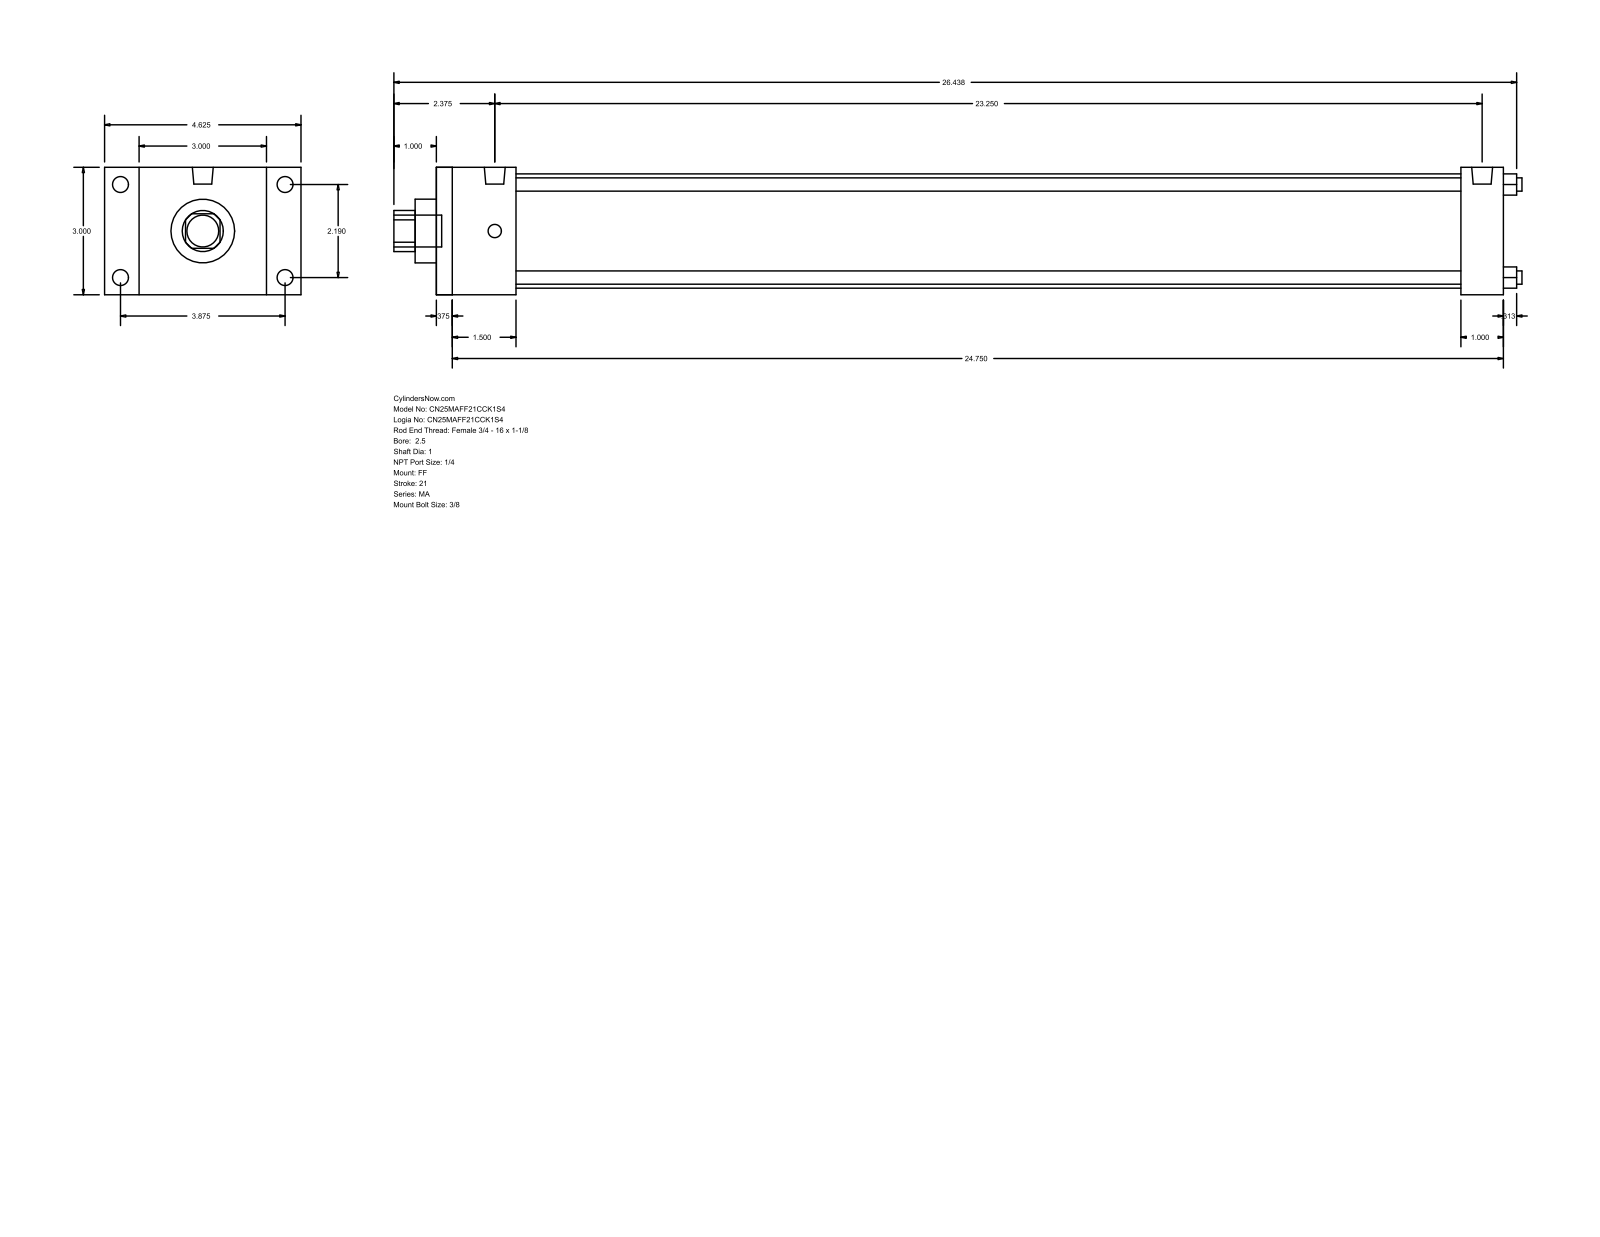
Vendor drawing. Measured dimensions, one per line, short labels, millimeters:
name: MA_FF__0250_1
written by: GSSL Pune (CONFIG_CONTROL_DESIGN)
unit: mm
bodies: 0 solids, 92 faces (64 planar, 28 cylindrical, 0 other)
size: 674.69 × 117.47 × 76.2
holes: 4× ⌀7.94, 1× ⌀25.4, 1× ⌀38.1, 1× ⌀68.33
bosses: 4× ⌀9.53, 4× ⌀7.94, 2× ⌀12.49, 1× ⌀19.05
rounds: 1× R12.29
face distances: 76.2, 638.18, 9.52, 628.66, 47.63, 612.77, 38.11, 603.25, 565.14, 590.55
hole spacings: 39.33, 55.62, 78.66
